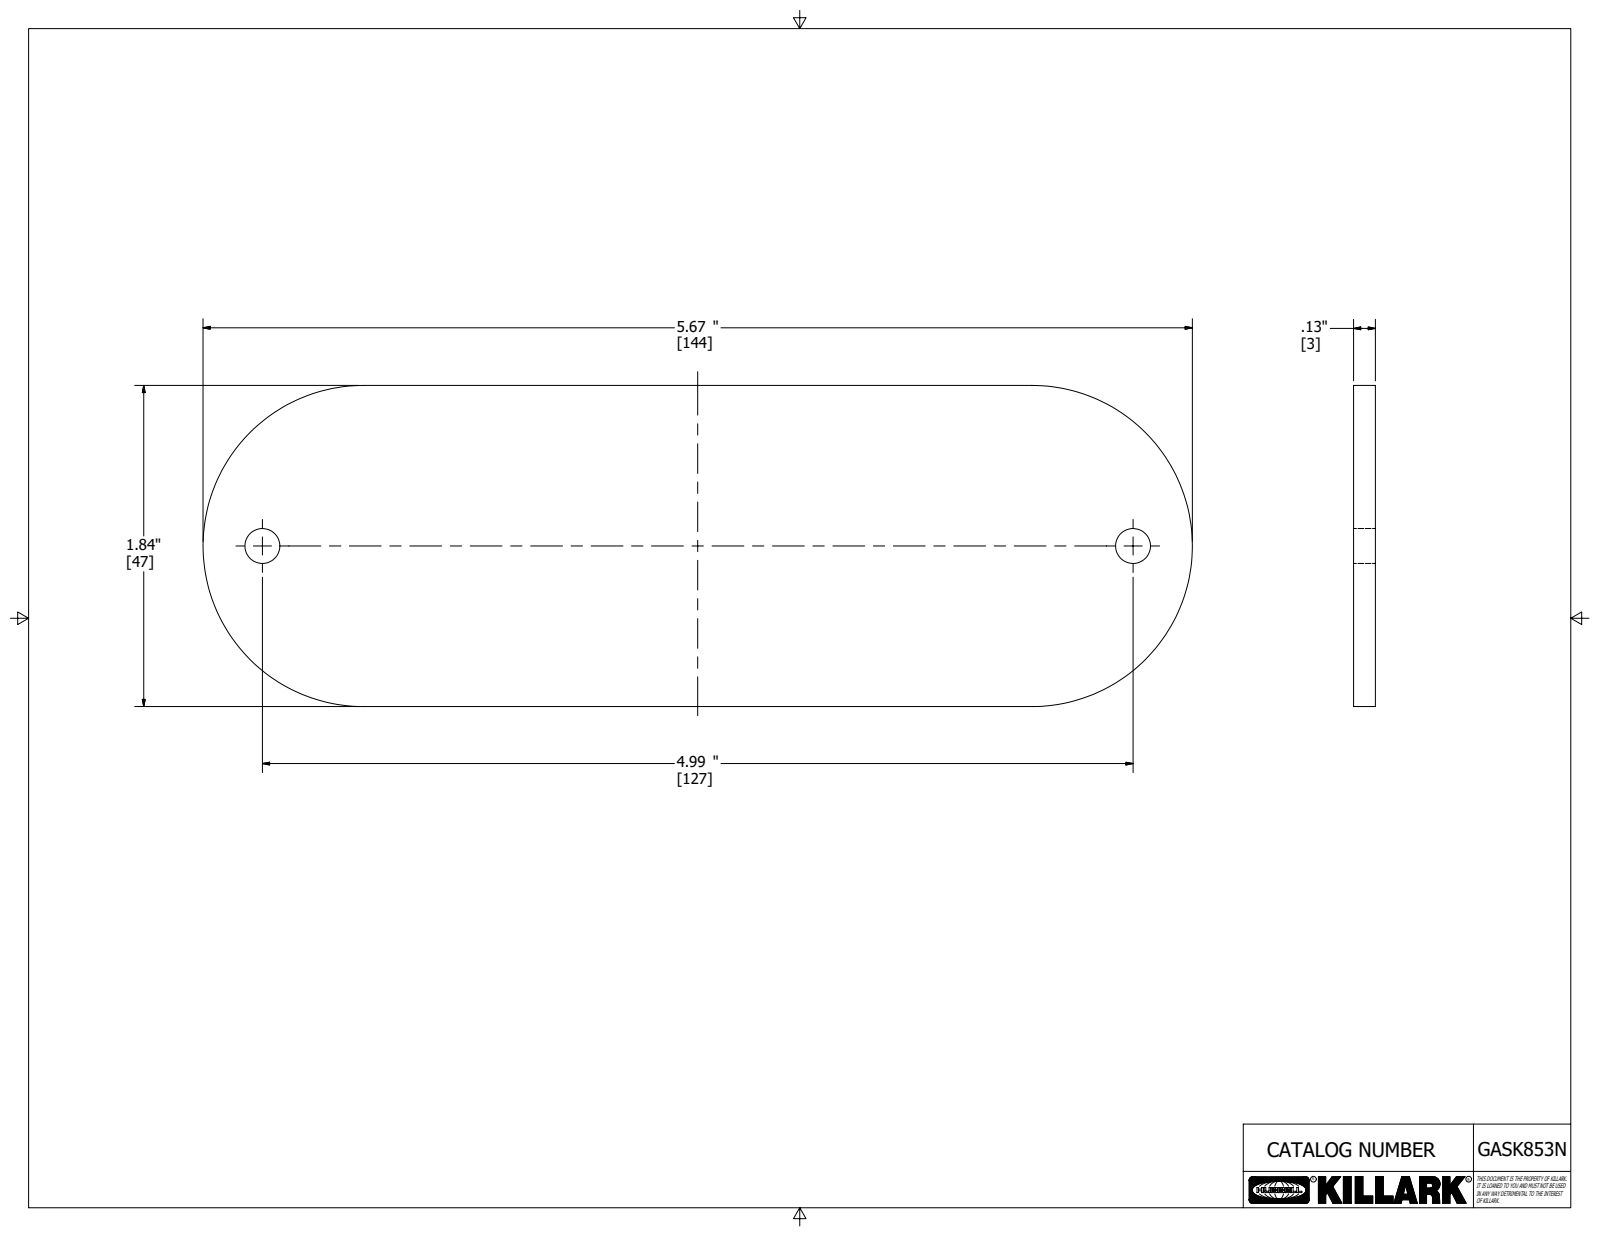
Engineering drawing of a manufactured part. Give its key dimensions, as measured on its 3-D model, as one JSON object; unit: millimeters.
{"part_name": "21778", "step_written_by": "Autodesk Inventor 2018 (AUTOMOTIVE_DESIGN)", "units": "millimeters", "bodies": {"solids": 1, "faces": 8, "planar": 4, "cylindrical": 4, "other": 0}, "overall_size": [144, 46.7, 3.2], "volume_mm3": 19750, "surface_area_mm2": 13630, "round_holes": [[5.1, 2]], "partial_cylinders_radius": [[23.4, 2]], "face_to_face_distances": [3.2, 46.7], "hole_center_spacings": [126.7]}
